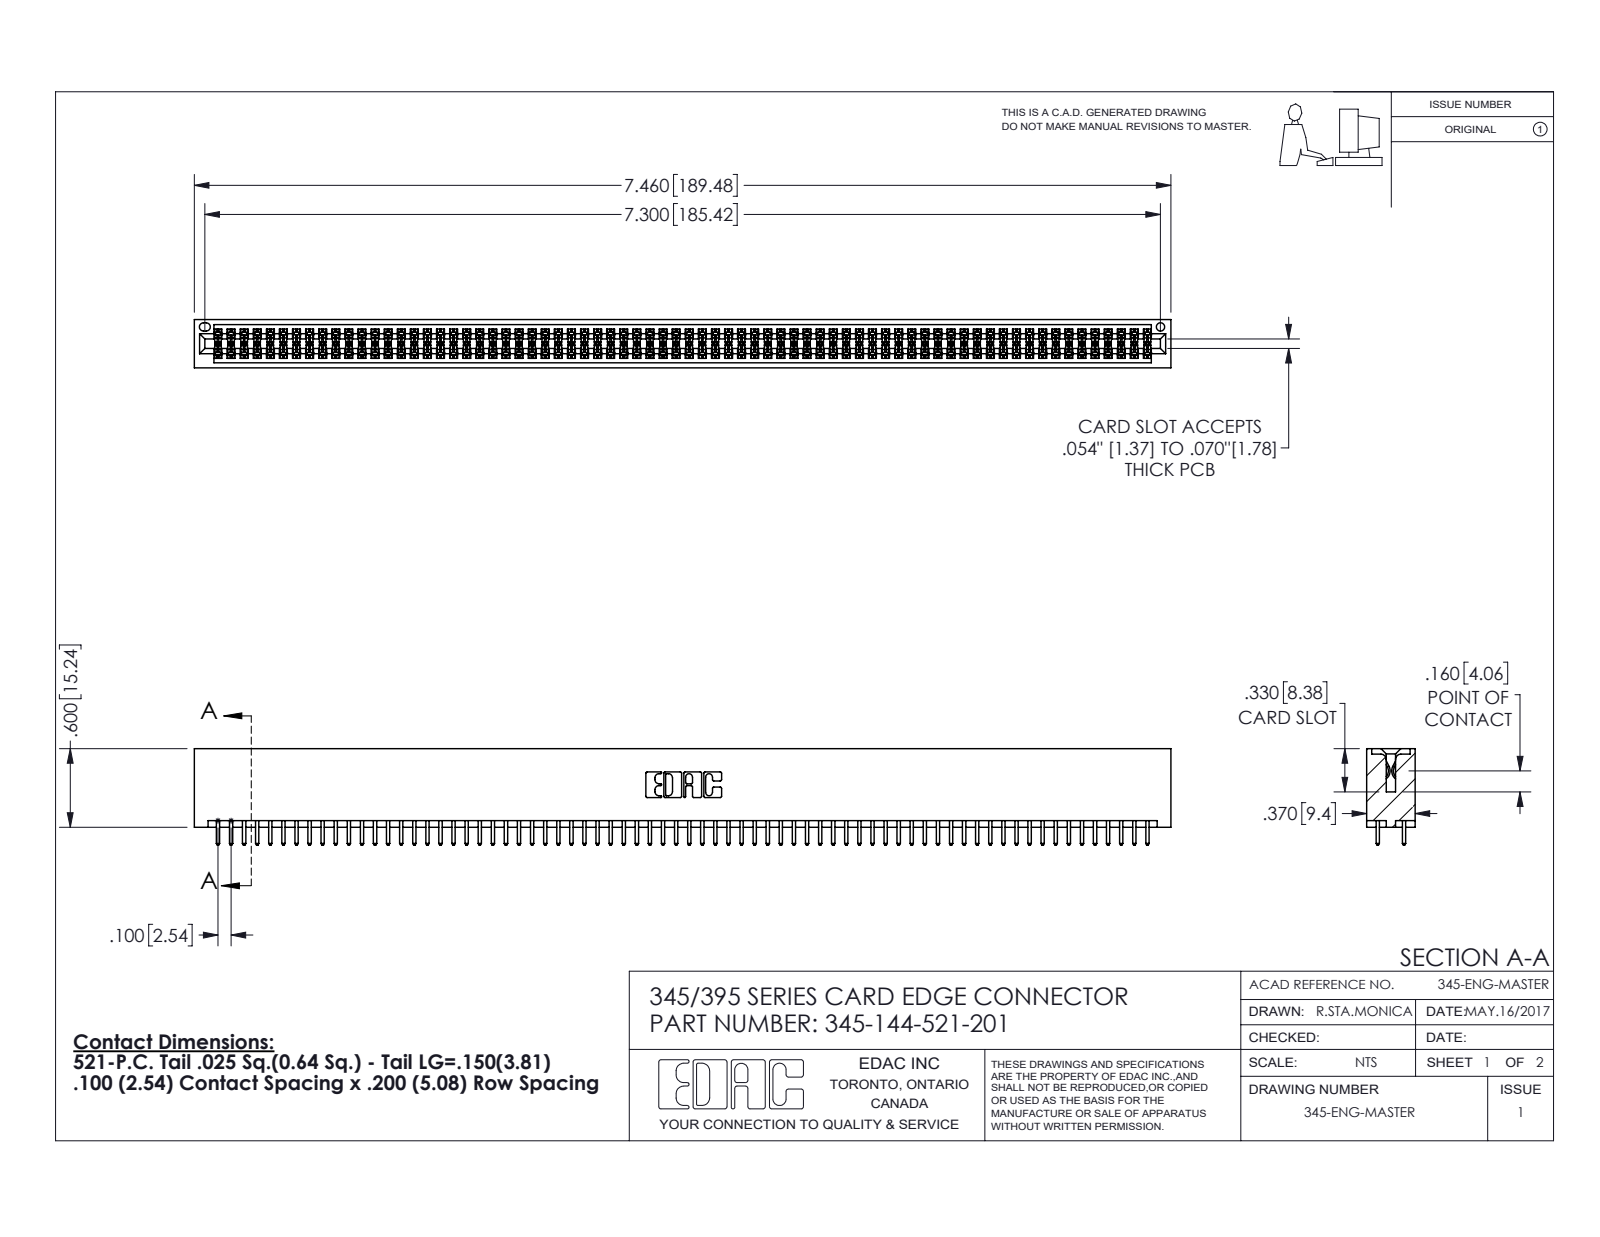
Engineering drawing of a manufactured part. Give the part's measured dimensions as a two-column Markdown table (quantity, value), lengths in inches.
| quantity | value |
| --- | --- |
| part name | 345-292-001_345-293-121; 345-144-521-201; 345 Part_No Mounting Lugs |
| STEP written by | SolidWorks 2016 (CONFIG_CONTROL_DESIGN) |
| units | inches |
| bodies | 145 solids, 7318 faces (4828 planar, 2490 cylindrical, 0 other) |
| overall size | 7.46 × 0.737 × 0.37 |
| volume | 1.174 in³ |
| surface area | 44.86 in² |
| round holes (diameter × count) | 0.064 × 1 |
| partial cylindrical surfaces (radius × count) | 0.006 × 216, 0.01 × 144, 0.01 × 22, 0.007 × 6, 0.031 × 6, 0.026 × 3, 0.014 × 2, 0.019 × 2 |
| main face-to-face distances | 0.298, 0.072, 0.2, 0.098, 0.272, 0.025, 0.37, 0.225, 0.175, 0.149 |
